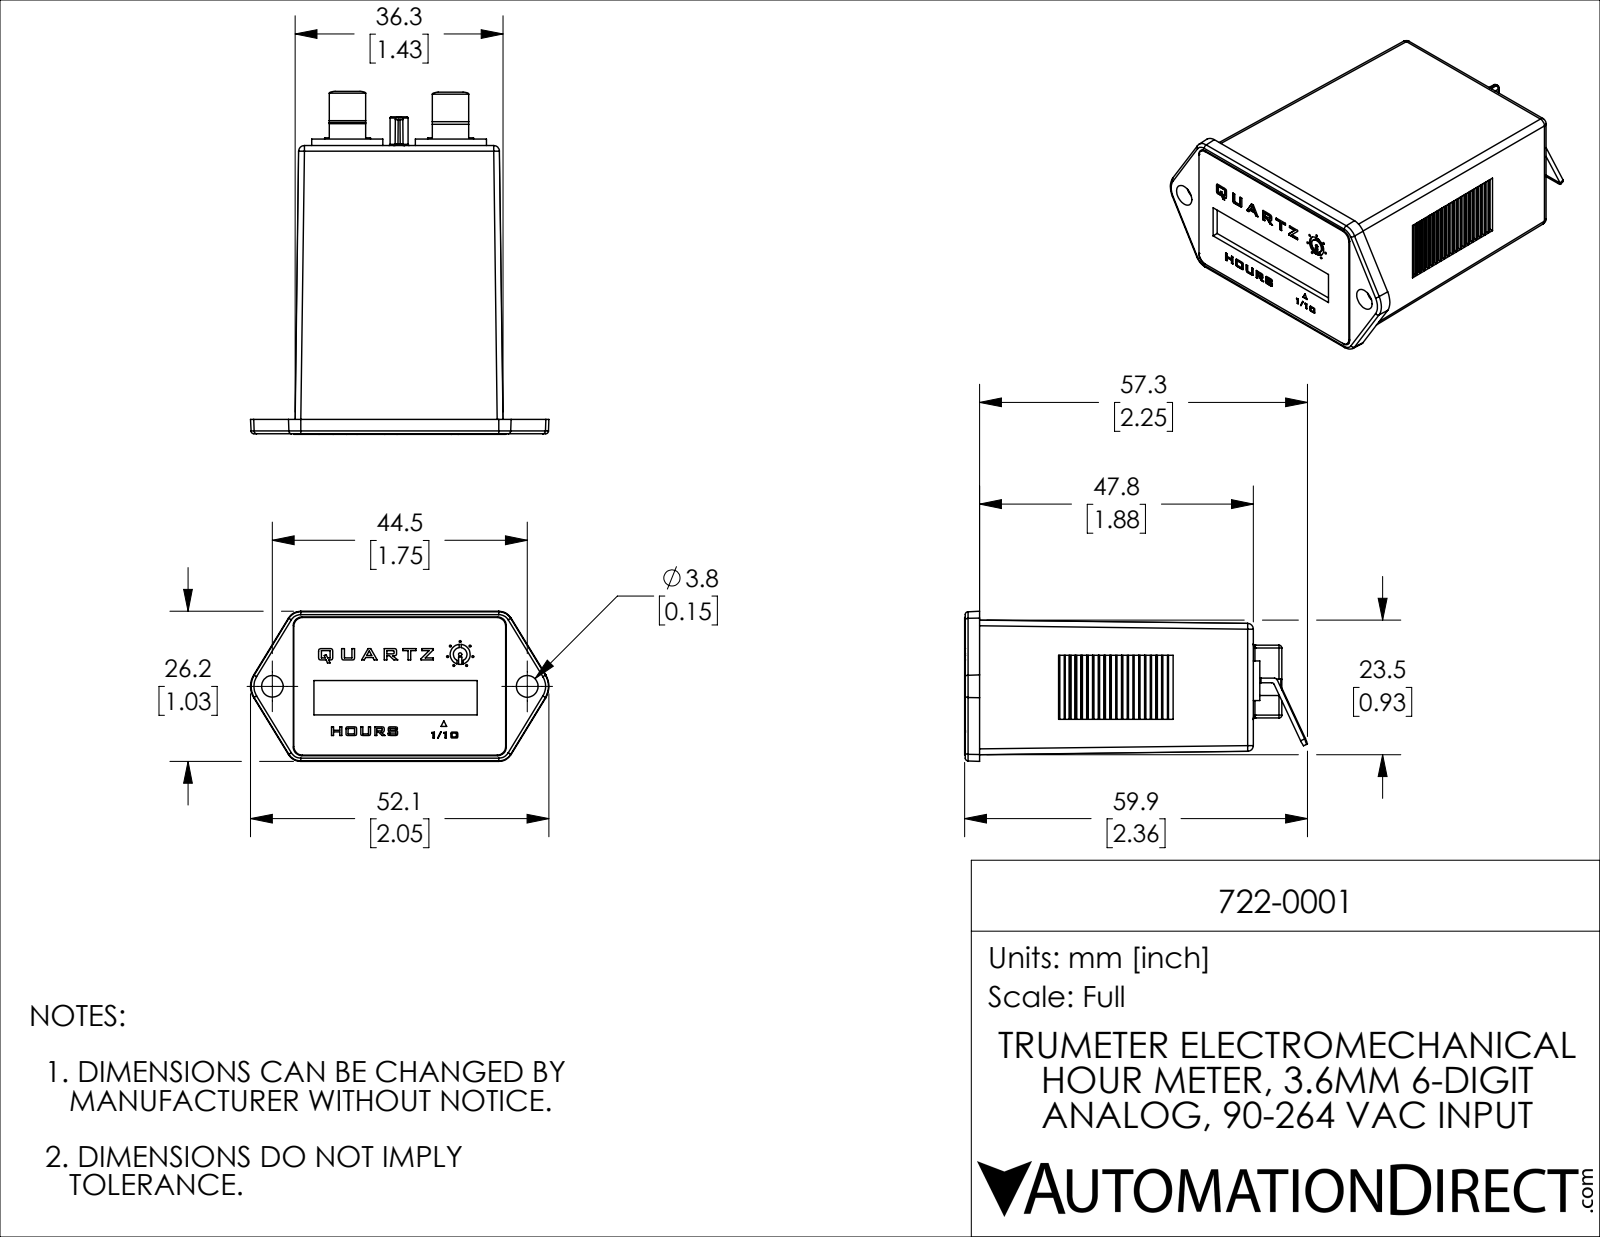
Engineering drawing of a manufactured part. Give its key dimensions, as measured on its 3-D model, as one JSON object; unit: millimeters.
{"part_name": "722-0001", "step_written_by": "SolidWorks 2021 (CONFIG_CONTROL_DESIGN)", "units": "millimeters", "bodies": {"solids": 5, "faces": 718, "planar": 536, "cylindrical": 126, "other": 56}, "overall_size": [59.86, 52.1, 26.2], "volume_mm3": 10688, "surface_area_mm2": 17145, "round_holes": [[0.34, 7], [1.5, 4], [0.56, 1], [3.51, 1], [3.77, 1], [3.8, 1]], "round_bosses_or_shafts": [[2.38, 1]], "partial_cylinders_radius": [[0.5, 32], [1, 17], [0.3, 15], [1.5, 10], [0.35, 4], [1.91, 2], [1.57, 1]], "face_to_face_distances": [1, 47.55, 48.55, 1.85, 50.4, 49.4, 1.6, 0.8, 2.6, 45.95], "hole_center_spacings": [2.24, 3.44, 1.9, 4.34, 2.25, 4.42, 1.89, 3.67]}
